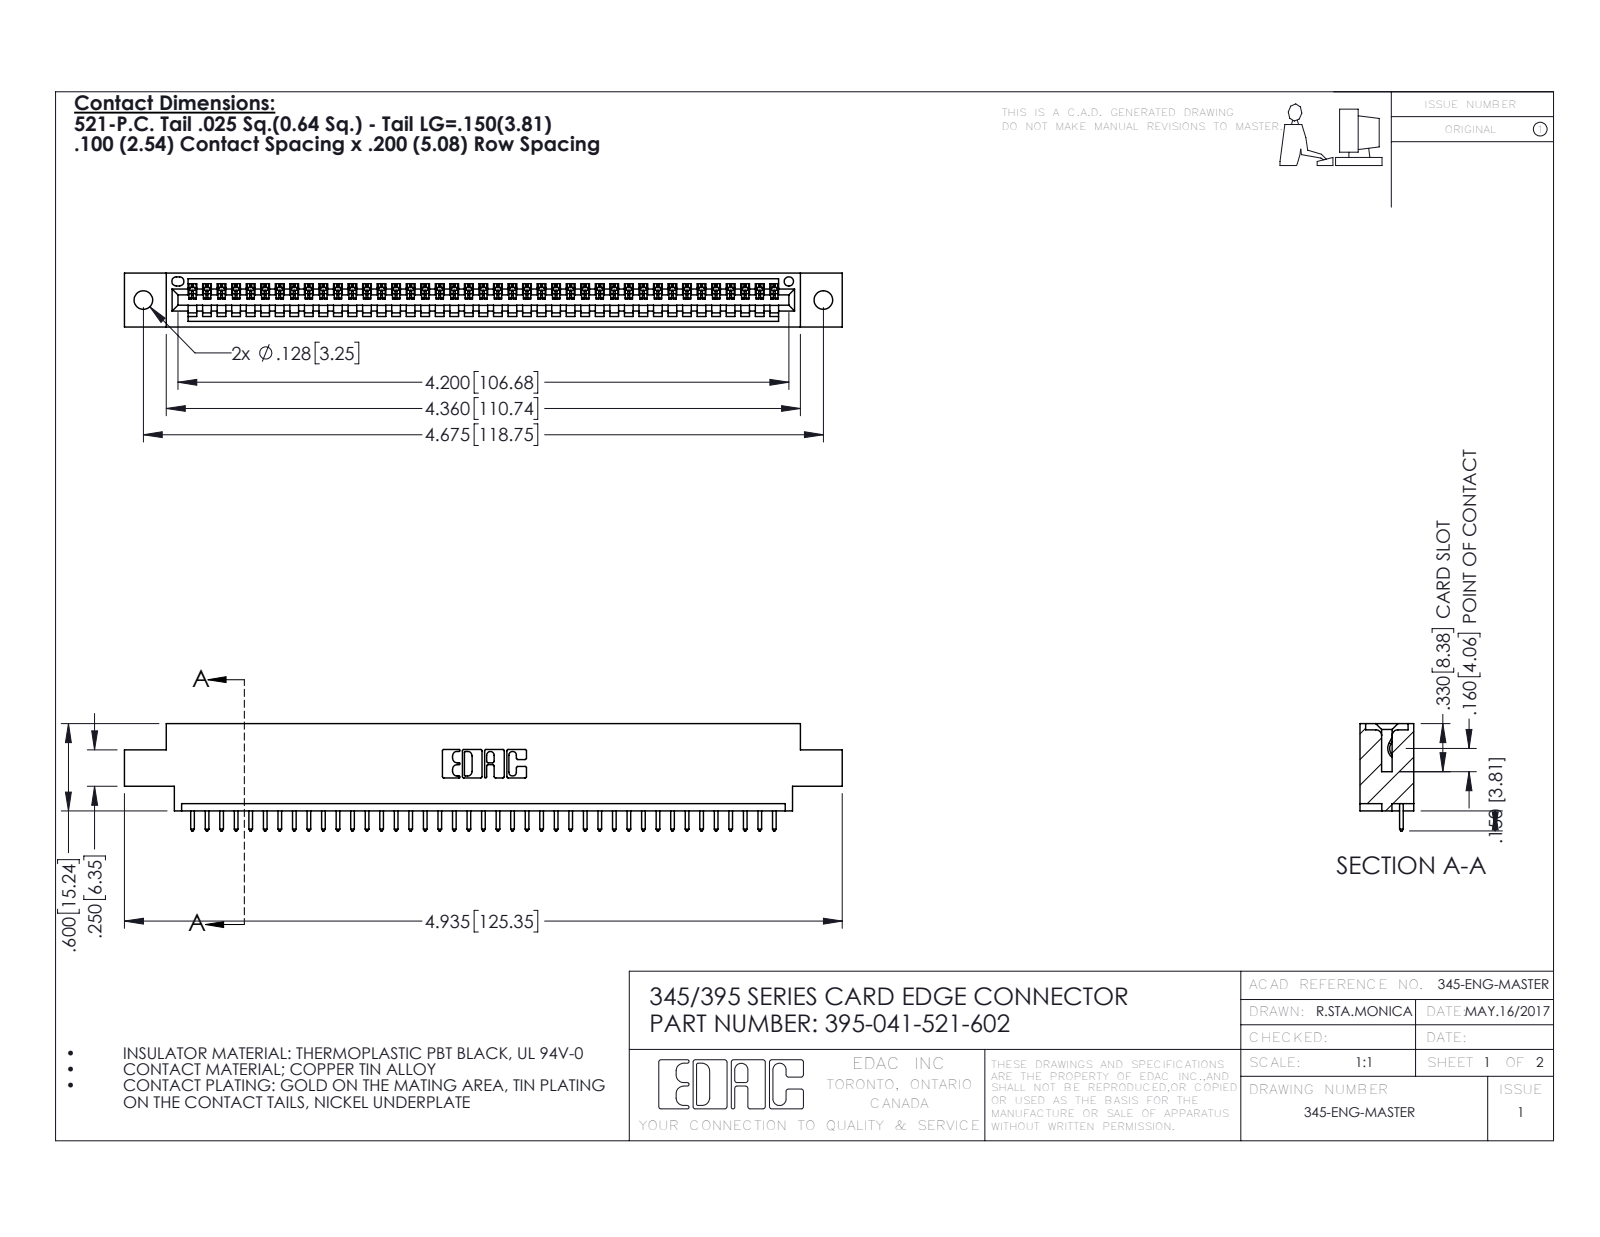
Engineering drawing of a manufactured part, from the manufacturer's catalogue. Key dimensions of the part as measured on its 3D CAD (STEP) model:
Part name (STEP PRODUCT): 395-041-521-602; 345-292-001_345-293-121; 345 Part_0.170 Offset - 0.128 Dia
STEP written by: SolidWorks 2016 (CONFIG_CONTROL_DESIGN)
Units: inches
Bodies: 42 solids, 2508 faces (1724 planar, 784 cylindrical, 0 other)
Overall size (bounding box): 4.935 × 0.737 × 0.37
Volume: 0.71 in³ · Surface area: 23 in²
Round holes (diameter × count): ⌀0.128 ×2, ⌀0.064 ×1
Partial cylindrical surfaces — rounded edges, fillets, slot ends (radius × count): R0.006 ×82, R0.01 ×82, R0.01 ×22, R0.007 ×6, R0.031 ×6, R0.026 ×3, R0.031 ×2, R0.04 ×2
Main face-to-face distances: 0.298, 0.072, 0.37, 0.2, 0.098, 0.272, 0.025, 0.225, 0.175, 0.149
Hole centre spacings: 0.27, 4.439, 4.675
